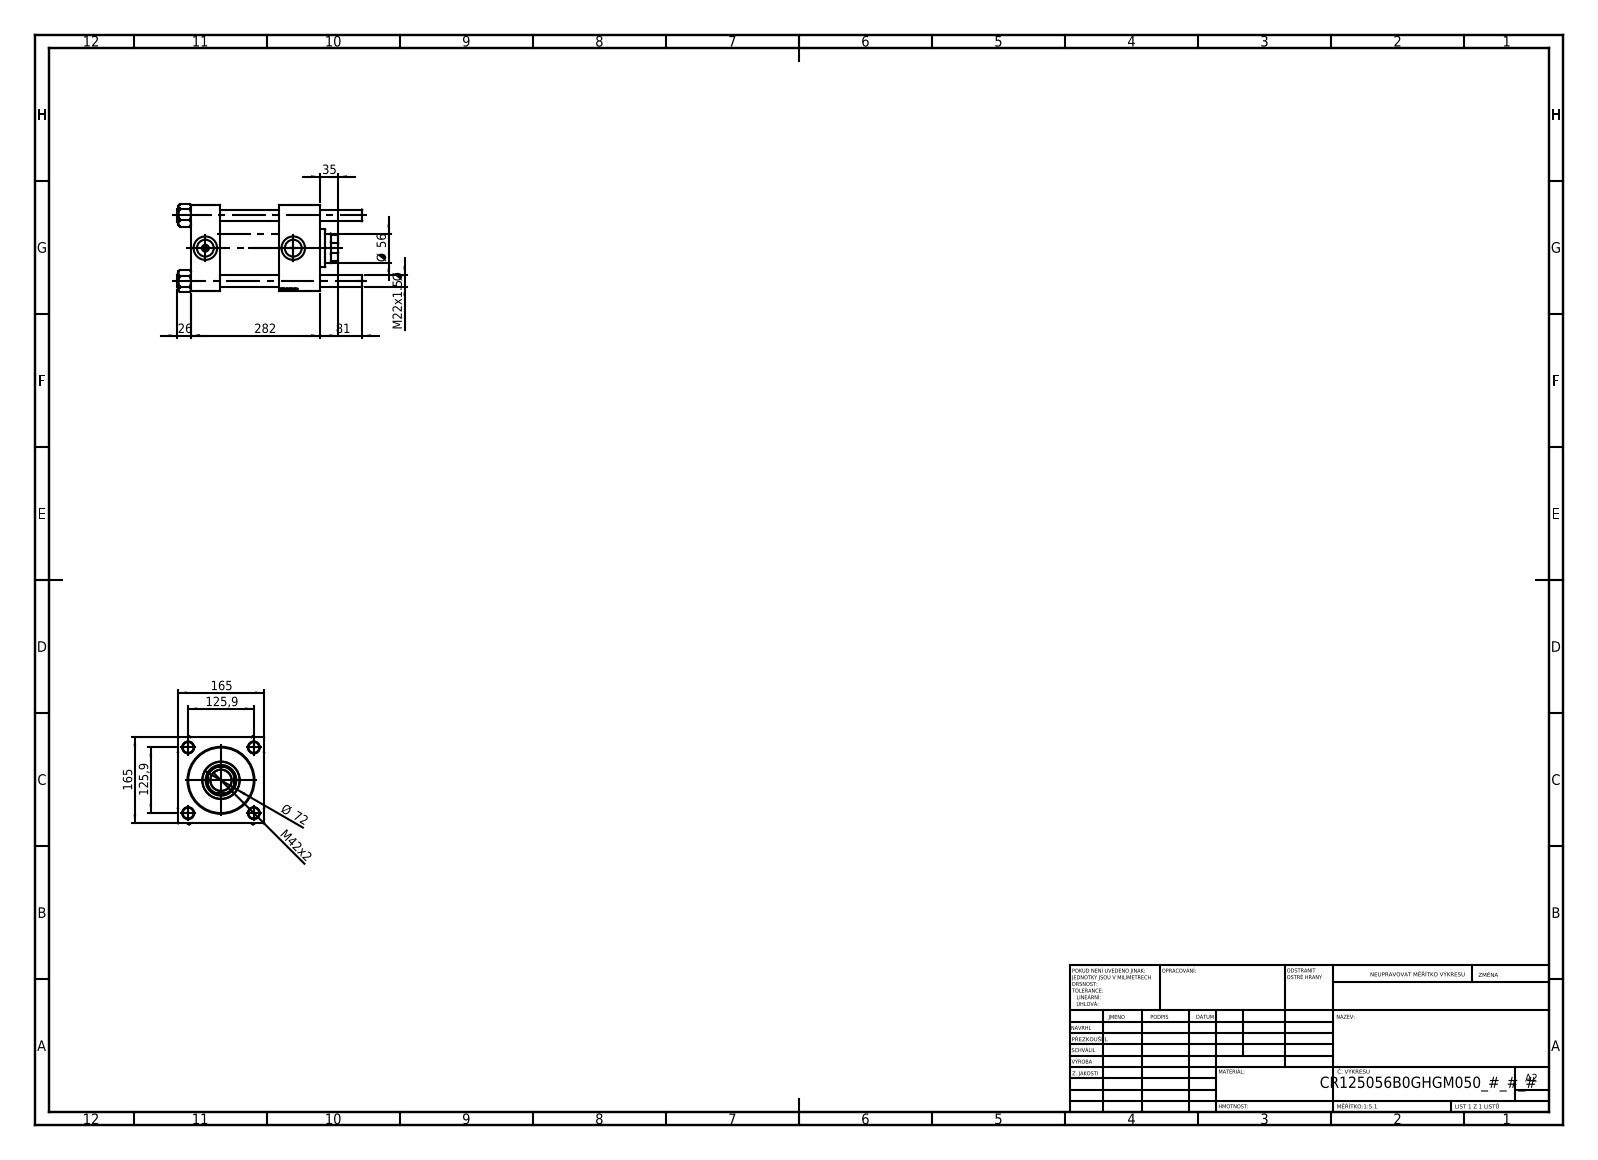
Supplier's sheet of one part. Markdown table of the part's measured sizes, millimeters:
| quantity | value |
| --- | --- |
| part name | V215CR_B_TYCINKA; V215CR_VCP_B; V215_VC_A; NUT_M5_B (+1 more) |
| STEP written by | SolidWorks 2019 (CONFIG_CONTROL_DESIGN) |
| units | millimeters |
| bodies | 11 solids, 1206 faces (480 planar, 78 cylindrical, 648 other) |
| overall size | 354 × 168.98 × 165.07 |
| volume | 4 836 000 mm³ |
| surface area | 586 095 mm² |
| round holes (diameter × count) | 22 × 4, 7 × 2, 32.24 × 2, 45 × 2, 40.5 × 1, 56 × 1, 59 × 1, 96 × 1, 125 × 1, 125.5 × 1 |
| round bosses / shafts (diameter × count) | 25 × 4, 131 × 1, 72 × 1 |
| partial cylindrical surfaces (radius × count) | 27 × 1 |
| main face-to-face distances | 165, 55, 247, 192, 114, 169, 78, 163.3, 218.3, 49.3 |
| hole center spacings | 89.02, 125.9, 178.05, 168.5 |
